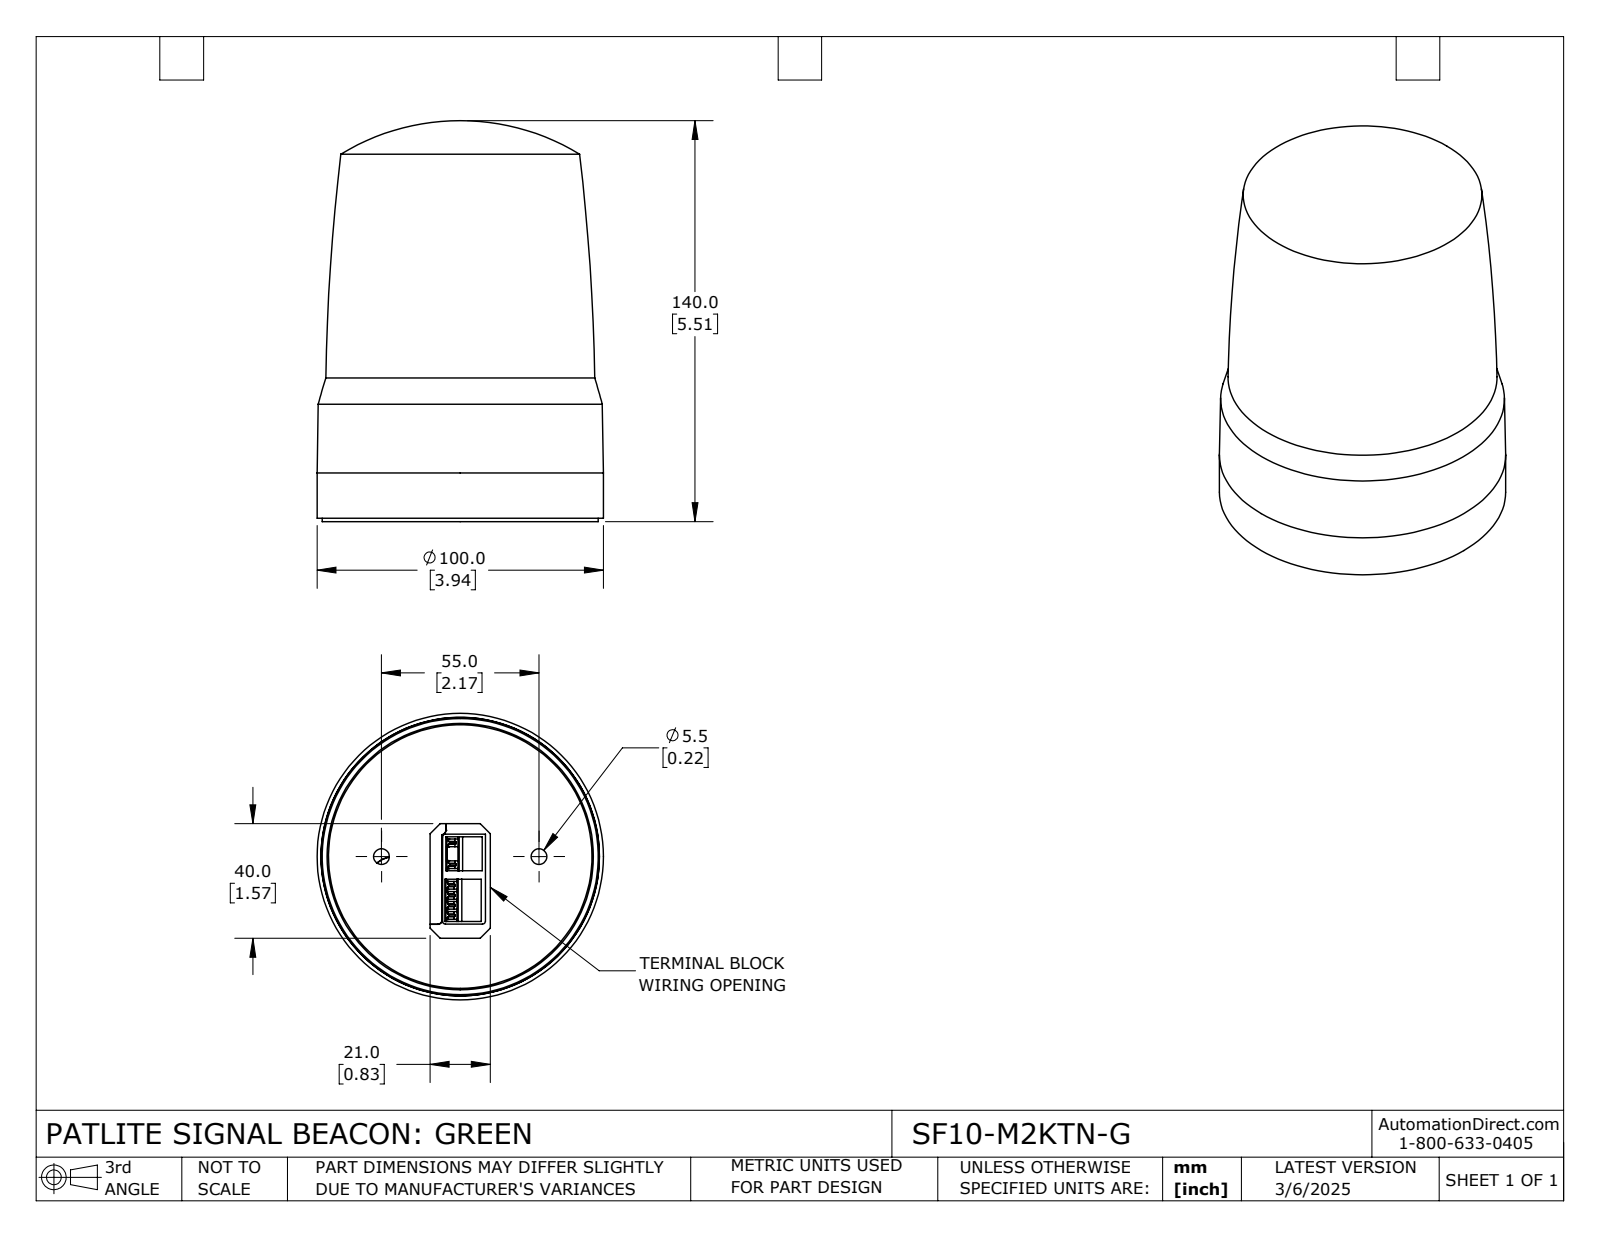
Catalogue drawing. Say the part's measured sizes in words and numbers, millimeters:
The part is named "SF10-M2KTN-G". Its 3-D file was written by "SolidWorks 2024 (CONFIG_CONTROL_DESIGN)". It is 2 solids with 268 faces: 183 planar, 29 cylindrical and 56 other. Overall it measures 140 by 100 by 100 millimeters. Its volume is 857 676 cubic millimeters and its surface area 76 986 square millimeters. Round holes: 2 of diameter 5.5, 2 of diameter 13, 1 of diameter 93, 1 of diameter 95.6. Round bosses or shafts: 1 of diameter 100, 1 of diameter 96.4, 1 of diameter 94.5, 1 of diameter 93.2, 1 of diameter 92. Partial cylindrical surfaces (rounded edges, fillets, slot ends): 2 of radius 0.3, 1 of radius 44.32, 1 of radius 44.75. The main face-to-face distances are 6.3, 14.7, 8.4, 1.5, 6.9, 13.2, 12.6, 3.15, 4.4, 7. The hole center spacings are 27.5, 55.
